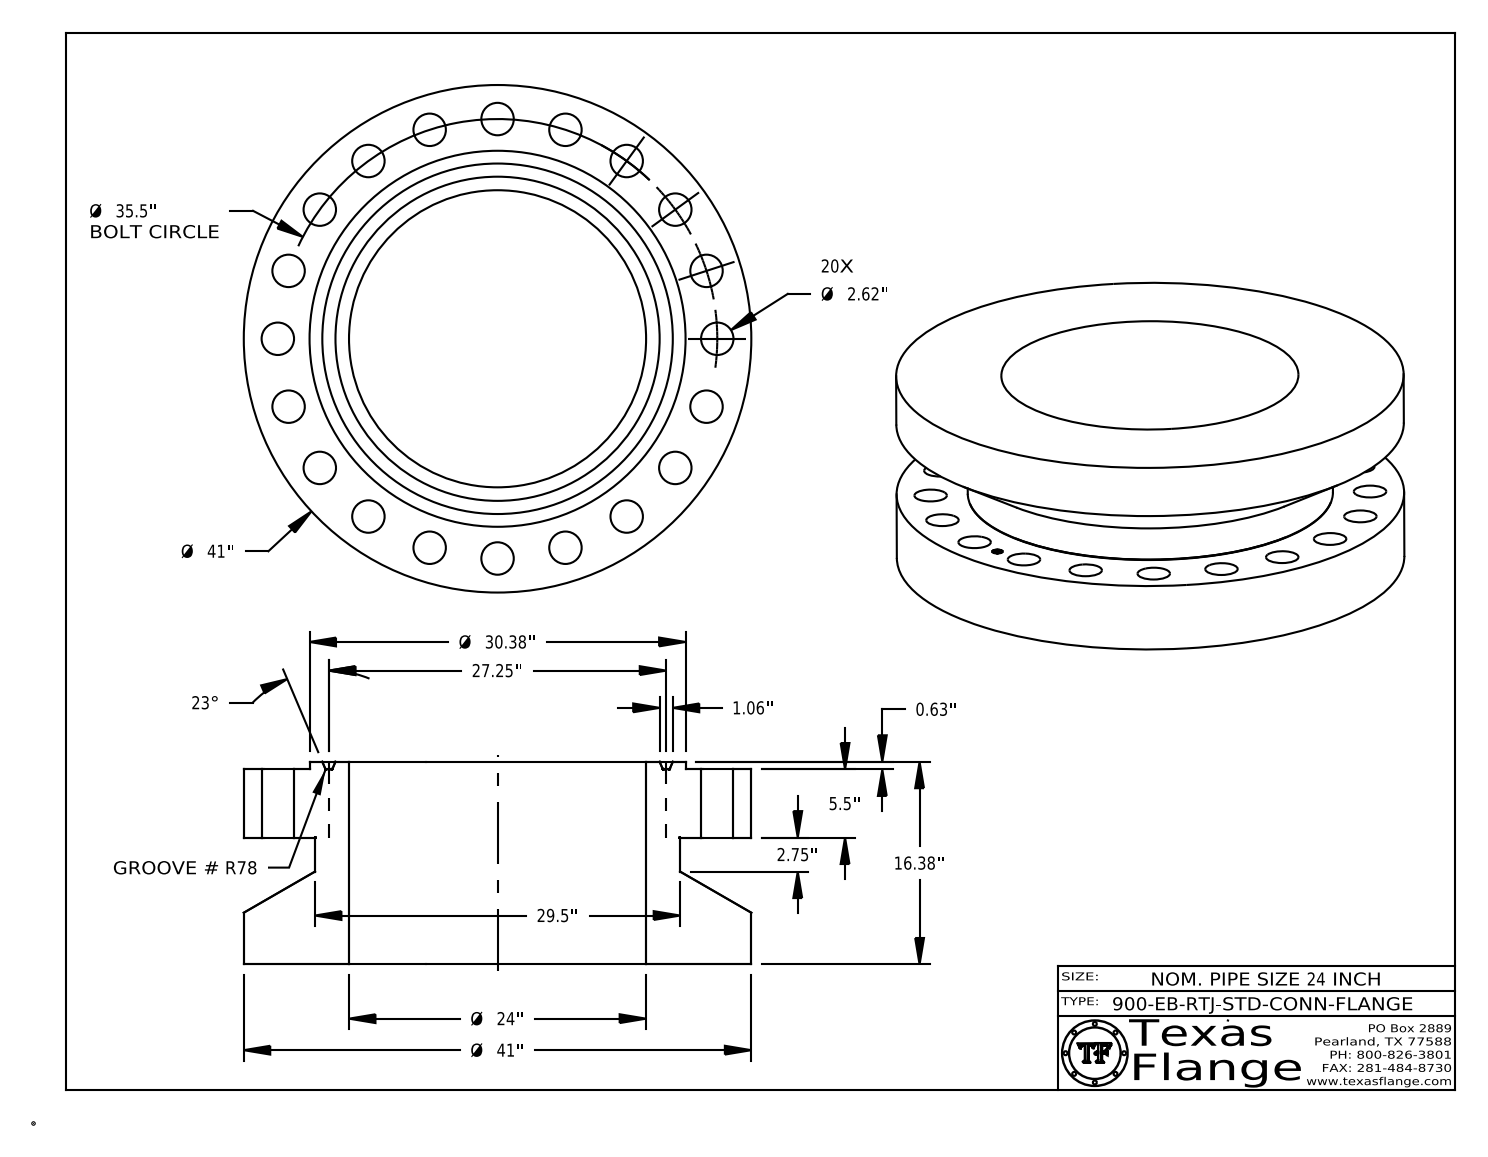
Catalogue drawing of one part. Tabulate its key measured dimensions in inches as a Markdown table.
| quantity | value |
| --- | --- |
| part name | 24-900-EB-RTJ-STD-CONN-FLANGE |
| STEP written by | CATIA V5 STEP AP214 (AUTOMOTIVE_DESIGN) |
| units | inches |
| bodies | 1 solid, 455 faces (371 planar, 70 cylindrical, 14 other) |
| overall size | 41 × 41 × 16.375 |
| volume | 10 338 in³ |
| surface area | 6 666 in² |
| round holes (diameter × count) | 2.62 × 20, 0.85 × 1, 24 × 1 |
| round bosses / shafts (diameter × count) | 0.051 × 8, 41 × 1, 30.375 × 1, 29.5 × 1, 0.67 × 1 |
| main face-to-face distances | 10.25, 5.5, 15.75, 0.625, 6.125, 16.375, 6.12, 5.495, 10.255, 0.254 |
| hole center spacings | 17.75, 10.97, 28.72, 31.631, 16.117, 20.866, 25.102, 33.762 |
